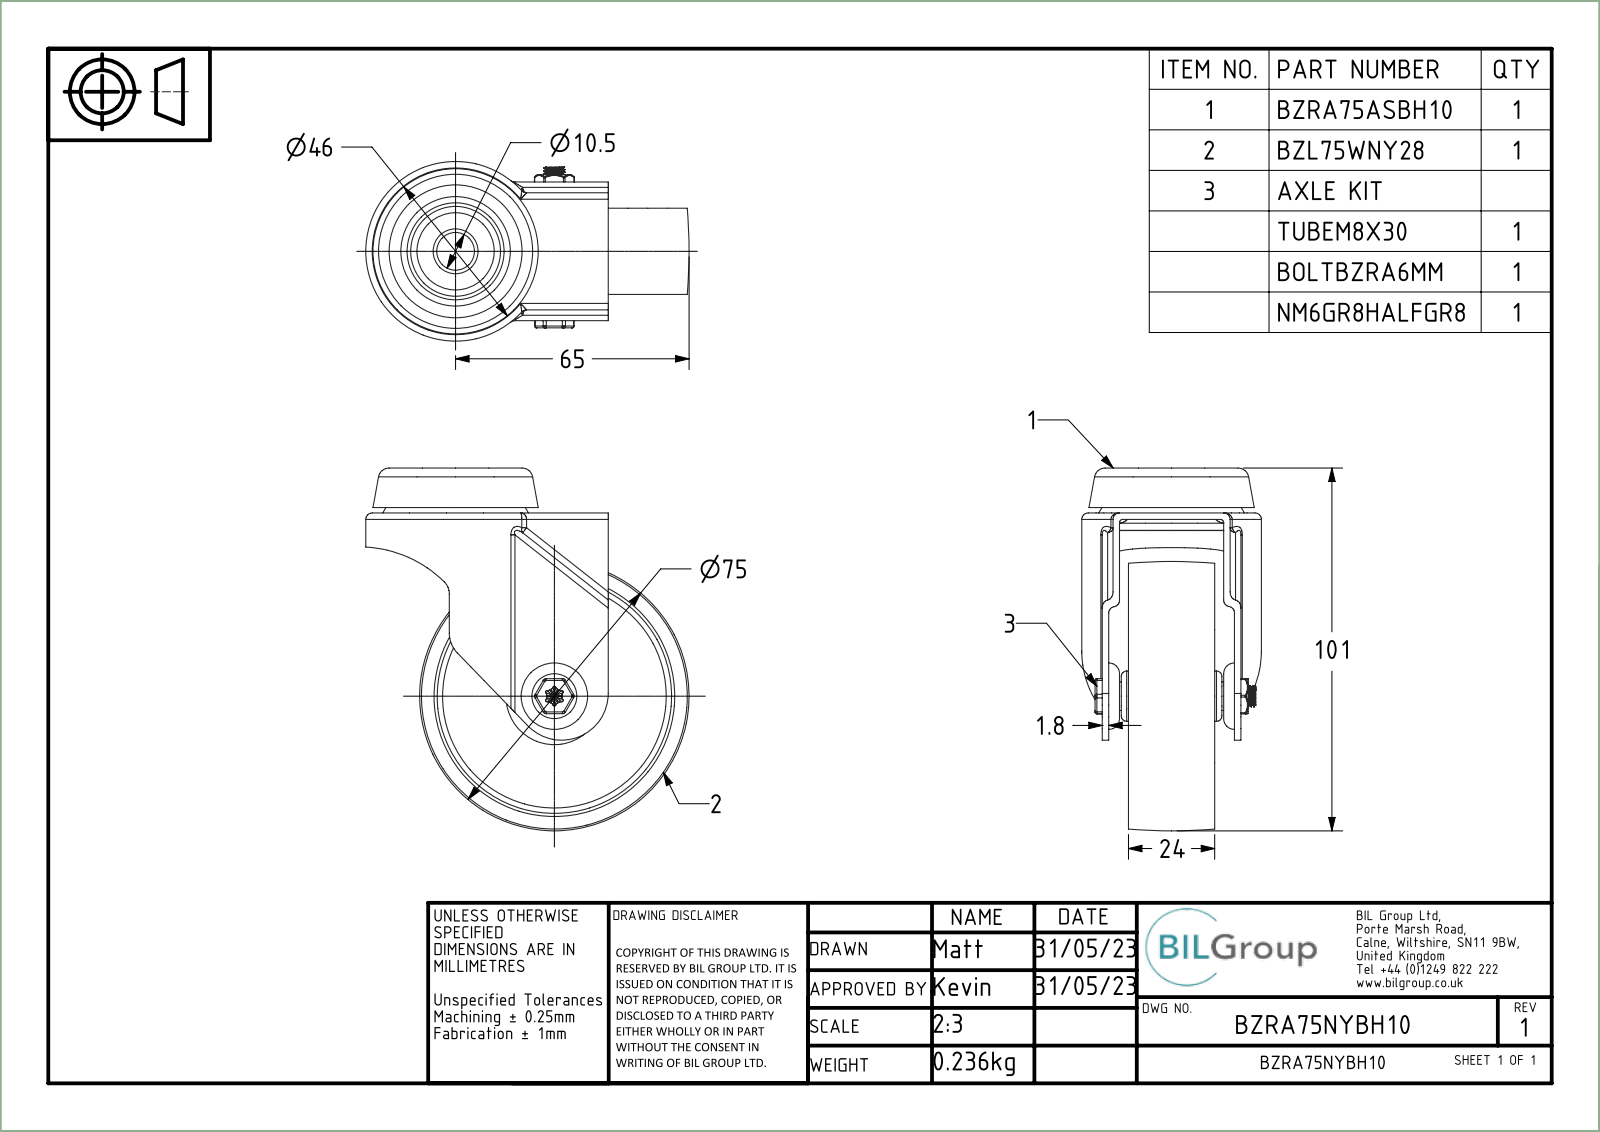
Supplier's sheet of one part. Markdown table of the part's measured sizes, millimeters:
| quantity | value |
| --- | --- |
| part name | BZRA75ASBH10; ZINC PLATED PRESSED STEEL FORKS; ZINC PLATED PRESSED STEEL HEAD; BZRA75NYBH10 (+8 more) |
| STEP written by | Spatial InterOp 3D (CONFIG_CONTROL_DESIGN) |
| units | millimeters |
| bodies | 6 solids, 386 faces (54 planar, 163 cylindrical, 169 other) |
| overall size | 101 × 90 × 50 |
| volume | 60 042 mm³ |
| surface area | 48 868 mm² |
| round holes (diameter × count) | 6 × 1, 6.3 × 1, 6.5 × 1, 8.2 × 1, 8.5 × 1, 10.5 × 1, 18 × 1, 19.5 × 1 |
| round bosses / shafts (diameter × count) | 22 × 1, 14 × 1, 8 × 1, 7.95 × 1, 5 × 1 |
| partial cylindrical surfaces (radius × count) | 1 × 18, 1.8 × 14, 0.5 × 12, 0.4 × 6, 0.9 × 6, 2.12 × 1, 4.63 × 1, 8 × 1 |
| main face-to-face distances | 1.8, 2, 3, 33.8, 20.3, 18.3, 11, 13, 7.3, 31.3 |
